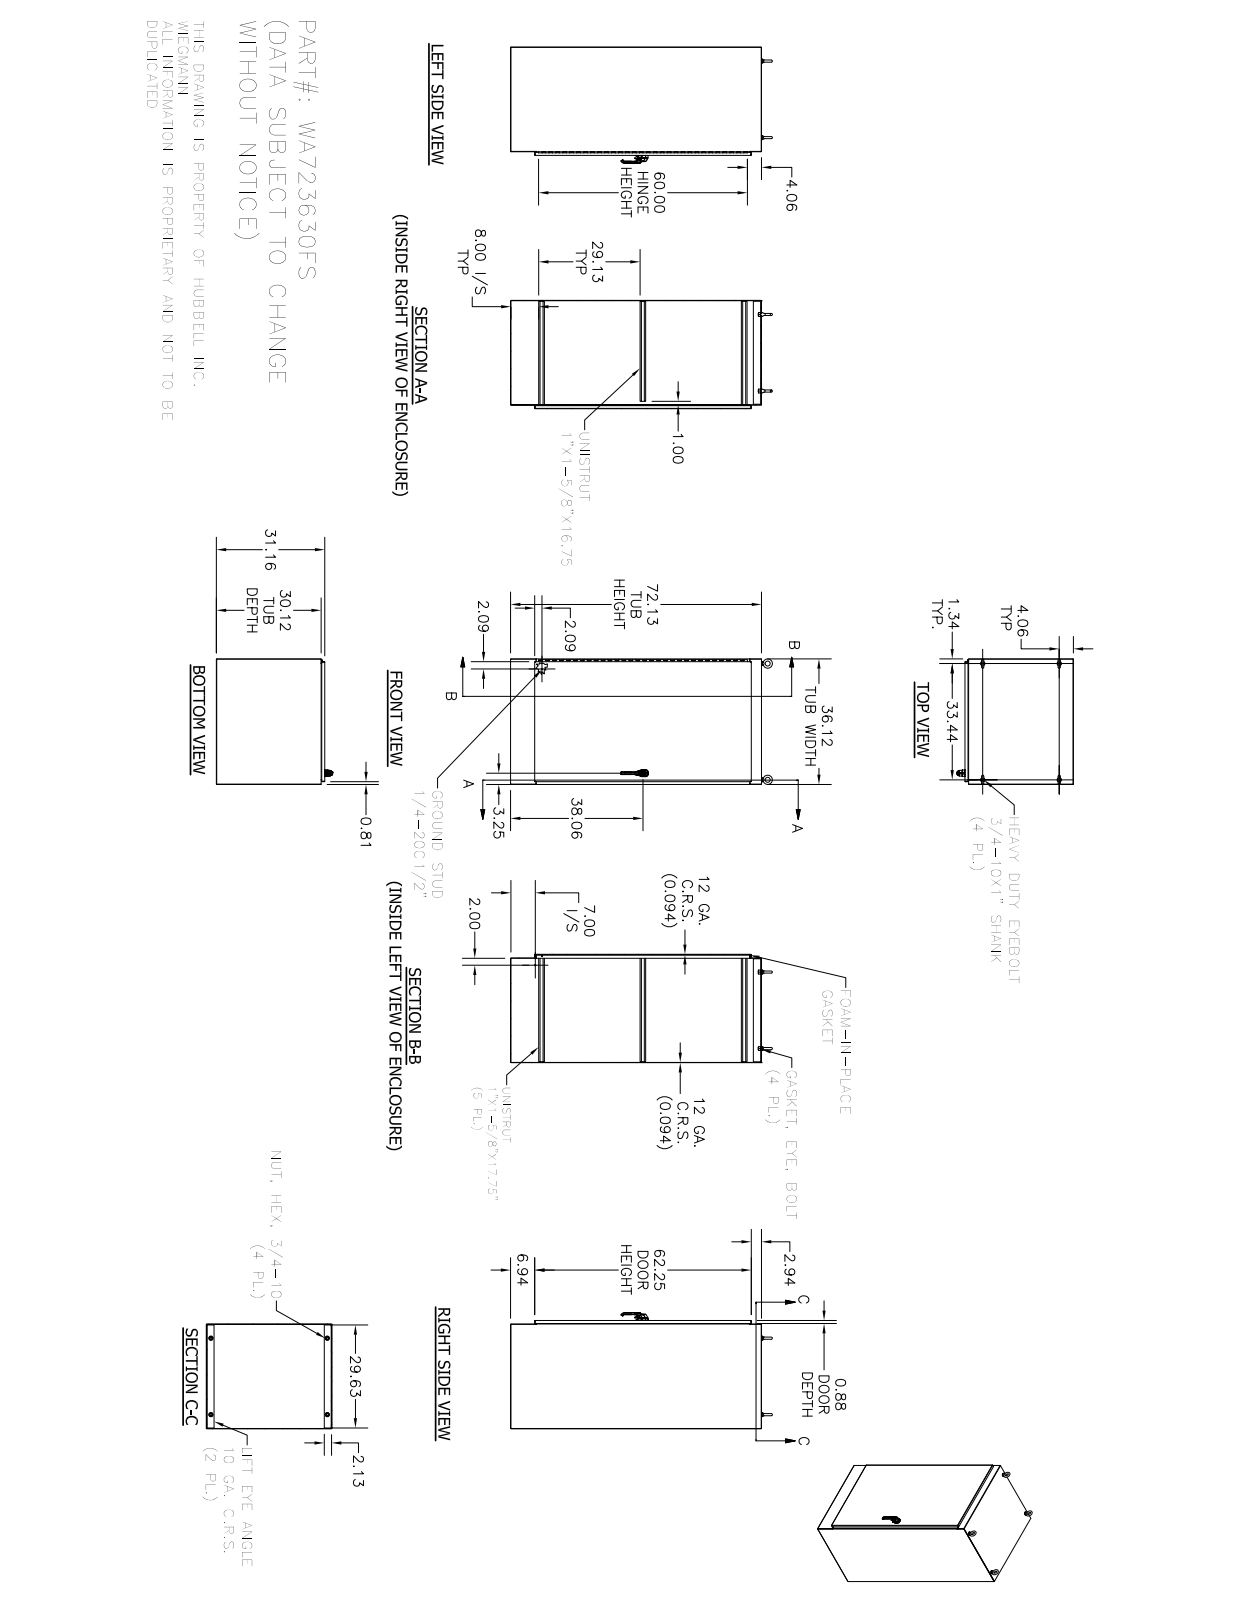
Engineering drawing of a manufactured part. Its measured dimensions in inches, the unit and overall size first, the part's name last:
Units: inches
Overall size (bounding box): 75.248 × 36.125 × 33.409
Round holes (diameter × count): ⌀0.276 ×8, ⌀0.2 ×4, ⌀0.642 ×4, ⌀0.813 ×4, ⌀0.213 ×3, ⌀0.28 ×3, ⌀0.315 ×2, ⌀0.402 ×2, ⌀0.407 ×2, ⌀0.413 ×2, ⌀0.122 ×1, ⌀0.124 ×1
Round bosses / shafts (diameter × count): ⌀1.25 ×4, ⌀1.12 ×4, ⌀0.75 ×4, ⌀0.25 ×3, ⌀0.531 ×2, ⌀0.526 ×2, ⌀0.435 ×2, ⌀0.337 ×2
Partial cylindrical surfaces — rounded edges, fillets, slot ends (radius × count): R0.02 ×178, R0.012 ×101, R0.019 ×23, R0.01 ×16, R0.031 ×14, R0.079 ×14, R0.019 ×12, R0.053 ×12
Main face-to-face distances: 0.094, 36.031, 31.067, 35.938, 36.125, 72.031, 30.973, 31.16, 71.938, 72.125
Hole centre spacings: 0.381, 0.381, 0.383, 0.762, 0.764, 0.886, 1.144, 1.271
Volume: 1 264 in³ · Surface area: 26 690 in²
Bodies: 53 solids, 3001 faces (1236 planar, 1025 cylindrical, 740 other)
Part name (STEP PRODUCT): WA7236FSFB; WA7230FSLS; WA7230FSRS; WA3630FSBTM (+8 more)
STEP written by: Autodesk Inventor 2014 (AUTOMOTIVE_DESIGN)
